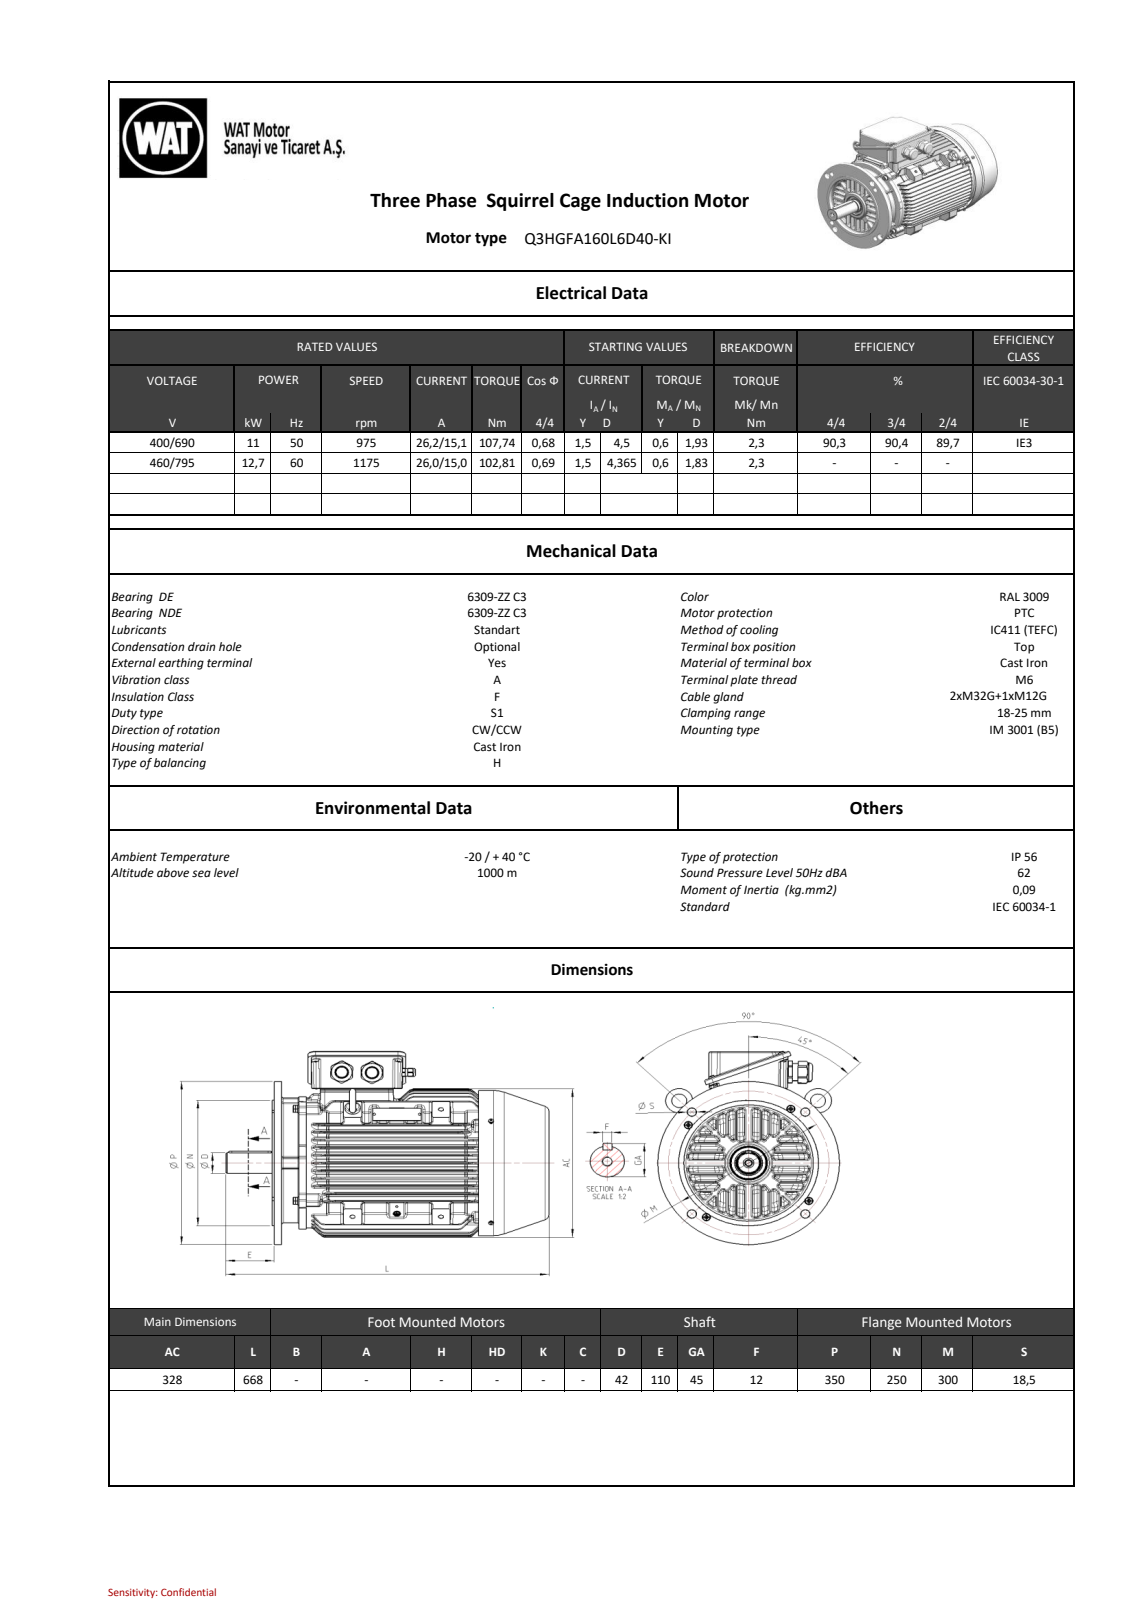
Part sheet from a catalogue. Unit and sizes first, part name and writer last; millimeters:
Units: millimetres
Overall size (bounding box): 667.5 × 402.41 × 350
Round holes (diameter × count): ⌀8.5 ×8, ⌀4.2 ×7, ⌀5.5 ×6, ⌀10.3 ×6, ⌀5.3 ×4, ⌀18.5 ×4, ⌀23 ×4, ⌀6.8 ×2, ⌀19 ×2, ⌀21 ×2, ⌀2.5 ×1, ⌀10 ×1
Round bosses / shafts (diameter × count): ⌀16 ×8, ⌀20 ×4, ⌀10 ×4, ⌀36 ×2, ⌀34.5 ×2, ⌀31.25 ×2, ⌀30 ×2, ⌀350 ×1
Partial cylindrical surfaces — rounded edges, fillets, slot ends (radius × count): R5 ×246, R1.5 ×112, R2 ×96, R4 ×94, R3 ×92, R1.8 ×58, R0.4 ×30, R37 ×24
Main face-to-face distances: 15.17, 137.45, 30.42, 122.2, 15.25, 45.73, 106.89, 30.56, 15.31, 61.11
Hole centre spacings: 136, 26.31, 144, 189.04, 203.65, 225.26, 292.89, 85.59
Bodies: 0 solids, 5492 faces (1050 planar, 1531 cylindrical, 2911 other)
Part name (STEP PRODUCT): C9017F38B806swhj
STEP written by: SIEMENS PLM Software NX 11.0 (AUTOMOTIVE_DESIGN)
